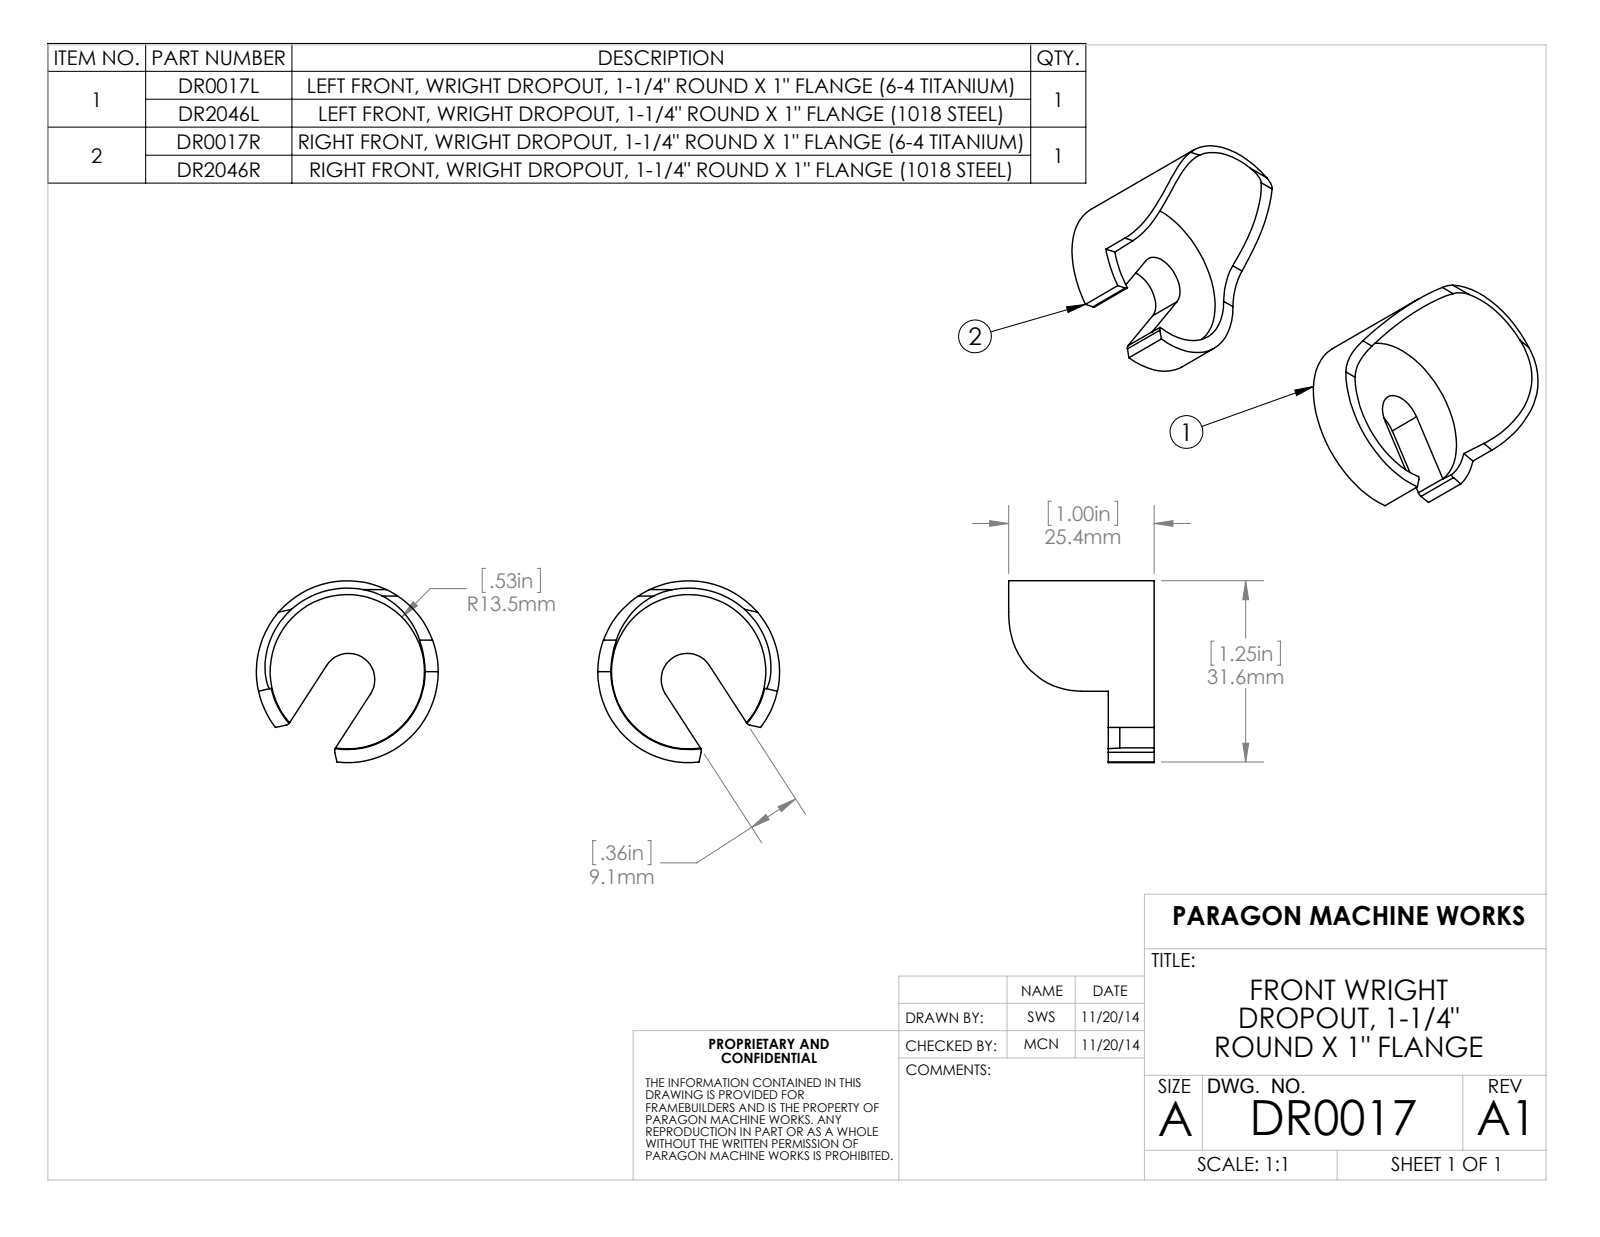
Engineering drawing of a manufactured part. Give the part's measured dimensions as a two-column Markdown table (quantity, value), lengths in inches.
| quantity | value |
| --- | --- |
| part name | DR0017R; DR0017L; DR0017 |
| STEP written by | SolidWorks 2014 (AUTOMOTIVE_DESIGN) |
| units | inches |
| bodies | 2 solids, 48 faces (22 planar, 20 cylindrical, 6 other) |
| overall size | 3.597 × 1.25 × 1 |
| volume | 0.652 in³ |
| surface area | 11.5 in² |
| round bosses / shafts (diameter × count) | 1.25 × 2 |
| partial cylindrical surfaces (radius × count) | 0.04 × 4, 0.18 × 2, 0.5 × 2, 0.05 × 1, 0.25 × 1 |
| main face-to-face distances | 0.236, 0.315, 0.079, 0.36, 0.36, 1, 0.764, 0.685 |
